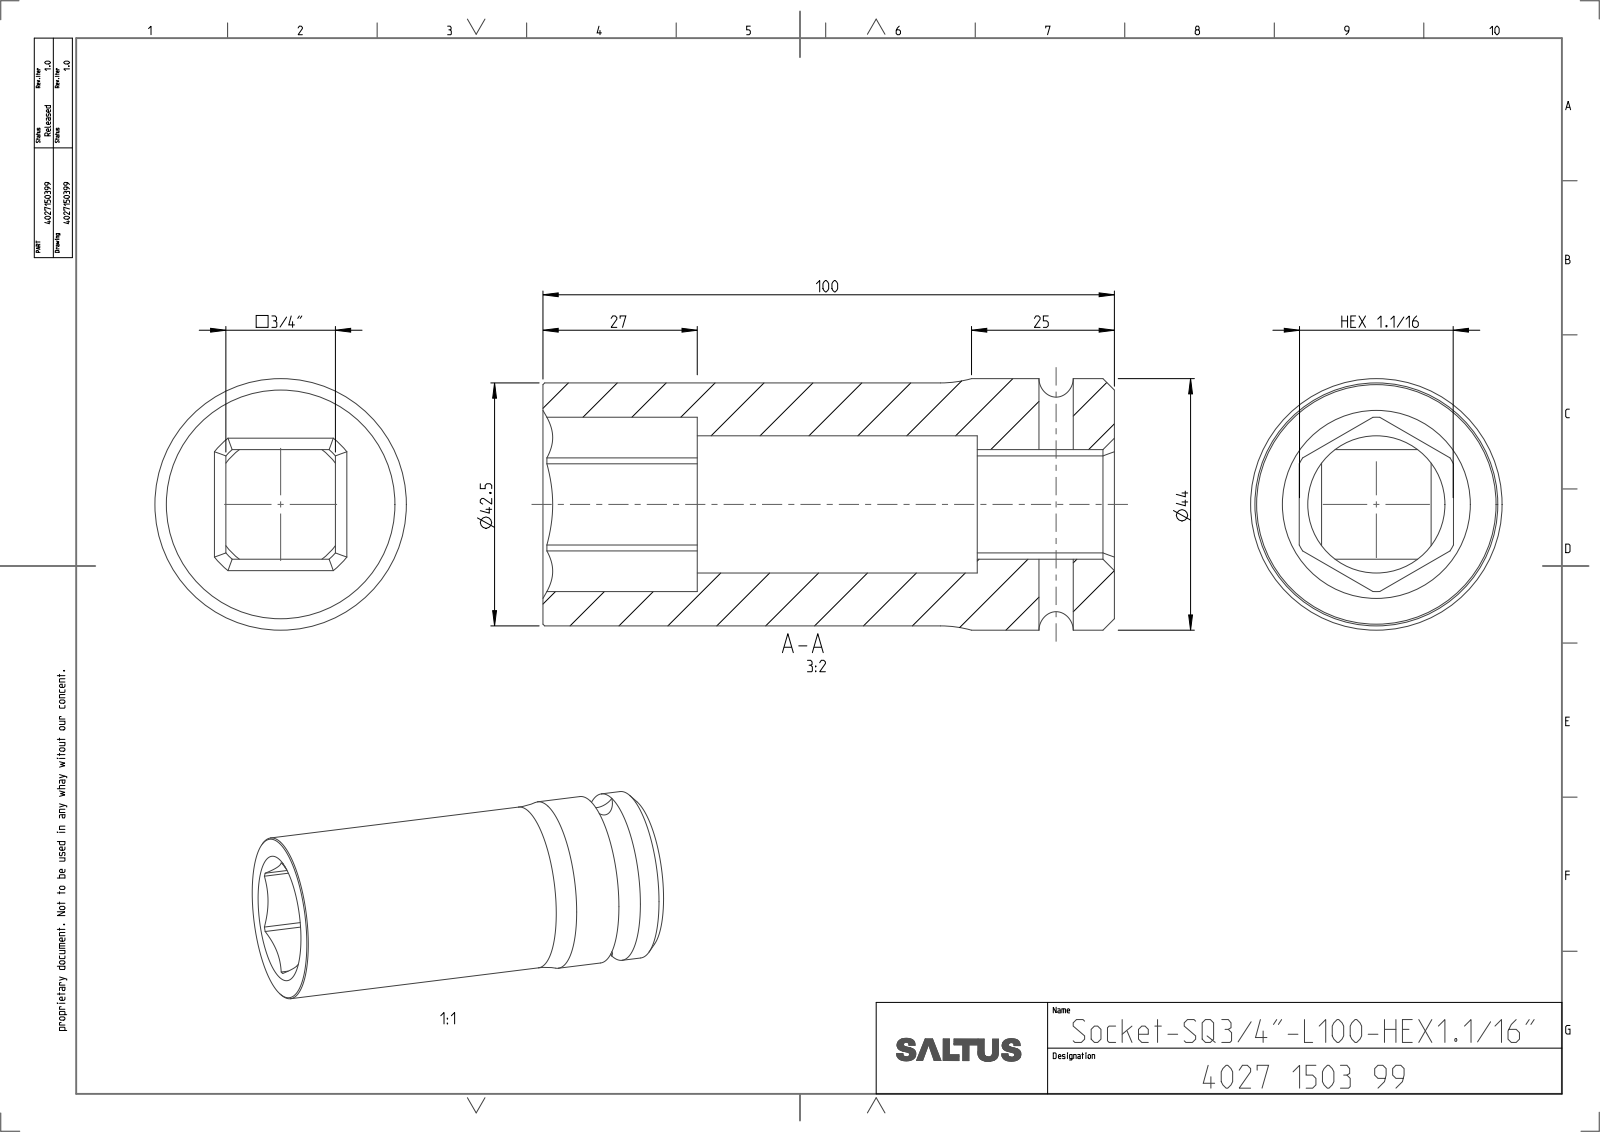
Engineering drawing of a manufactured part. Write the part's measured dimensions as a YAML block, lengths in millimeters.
part_name: "4027150399"
step_written_by: "CREO PARAMETRIC BY PTC INC, 2022414 (CONFIG_CONTROL_DESIGN)"
units: millimeters
bodies: {solids: 1, faces: 54, planar: 18, cylindrical: 22, other: 14}
overall_size: [100, 44, 44]
volume: 89834
surface_area: 24236
round_holes:
  - {diameter: 6, count: 1}
  - {diameter: 26, count: 1}
round_bosses_or_shafts:
  - {diameter: 44, count: 1}
  - {diameter: 42.5, count: 1}
partial_cylinders:
  - {radius: 12.8, count: 1}
  - {radius: 15.25, count: 1}
face_to_face_distances: [26.98, 3.9, 23.08, 19.18, 100, 24, 76, 73, 49, 27]
